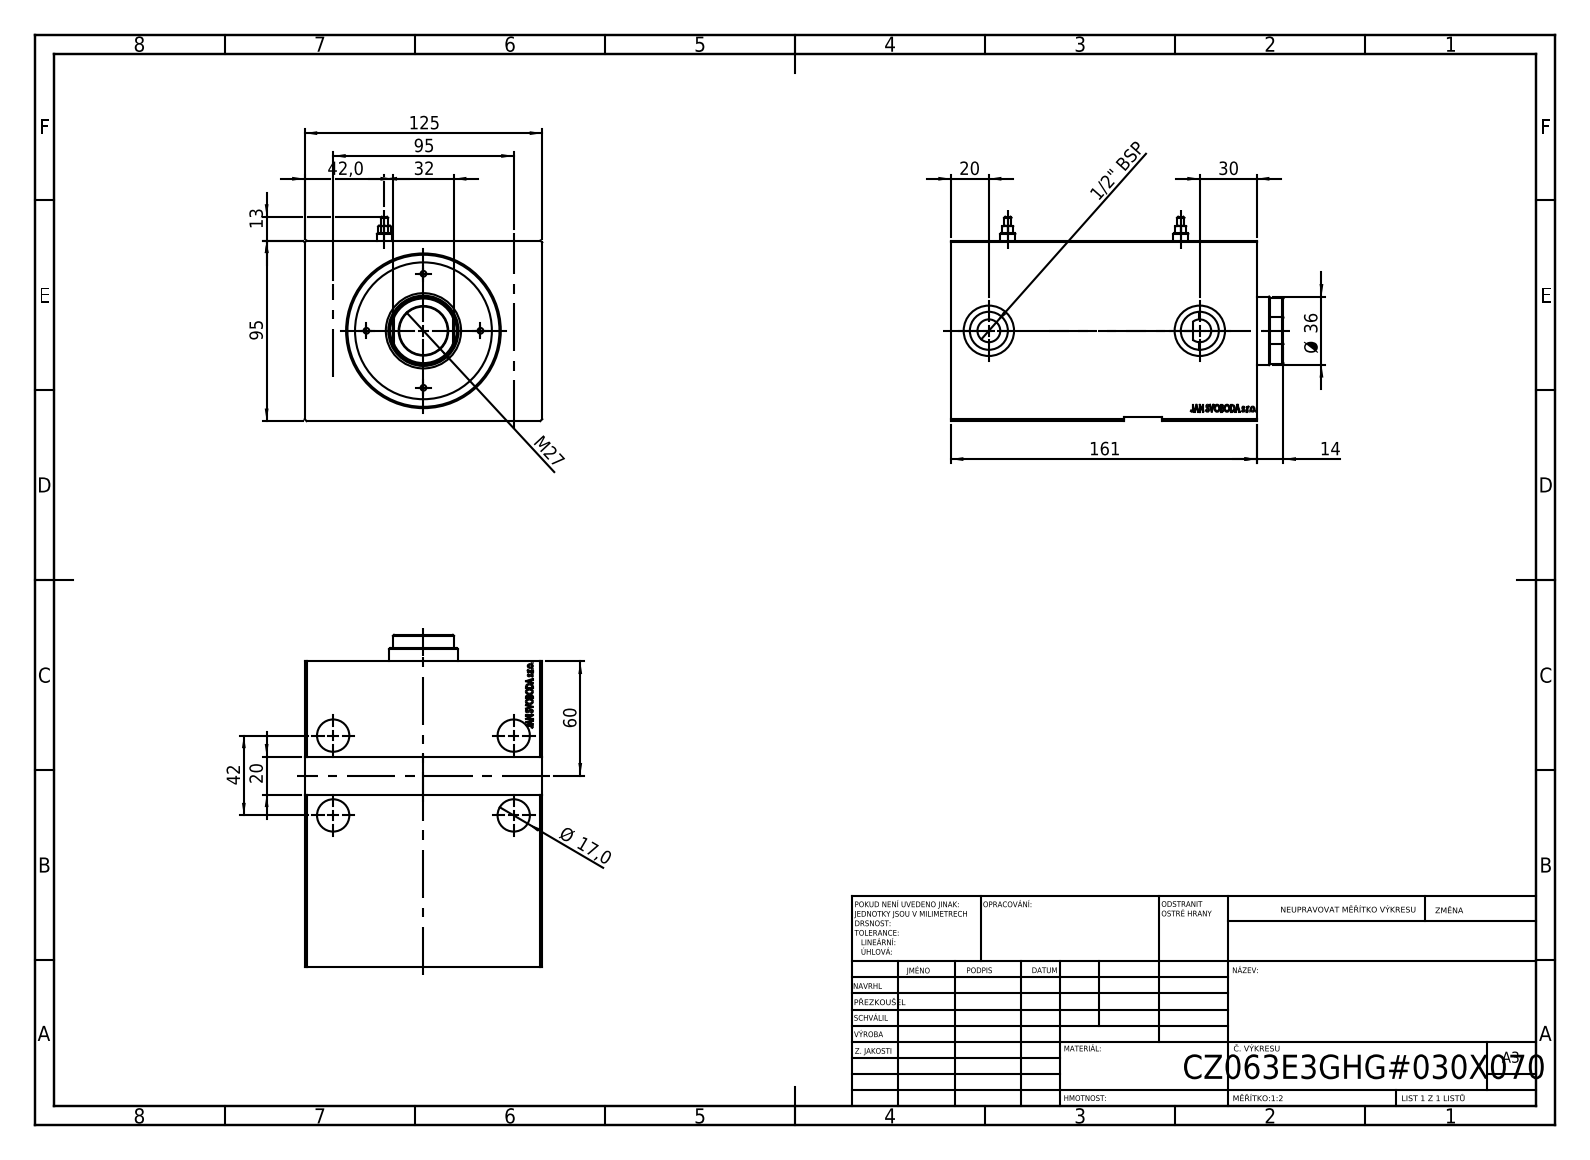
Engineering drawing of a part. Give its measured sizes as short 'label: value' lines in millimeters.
written by: SolidWorks 2019 (CONFIG_CONTROL_DESIGN)
unit: mm
bodies: 1 solid, 805 faces (393 planar, 30 cylindrical, 382 other)
size: 161 × 125 × 95
volume: 1 347 000 mm³; area: 143 284 mm²
holes: 4× ⌀17, 2× ⌀8, 2× ⌀20, 2× ⌀26.5, 1× ⌀12, 1× ⌀36, 1× ⌀63, 1× ⌀80
rounds: 1× R6
face distances: 95, 125, 161, 140.2, 20.8, 2, 93, 14, 126.2, 147
hole spacings: 42, 95, 103.87, 27.02, 49.09, 56.82, 68.01, 79.4
